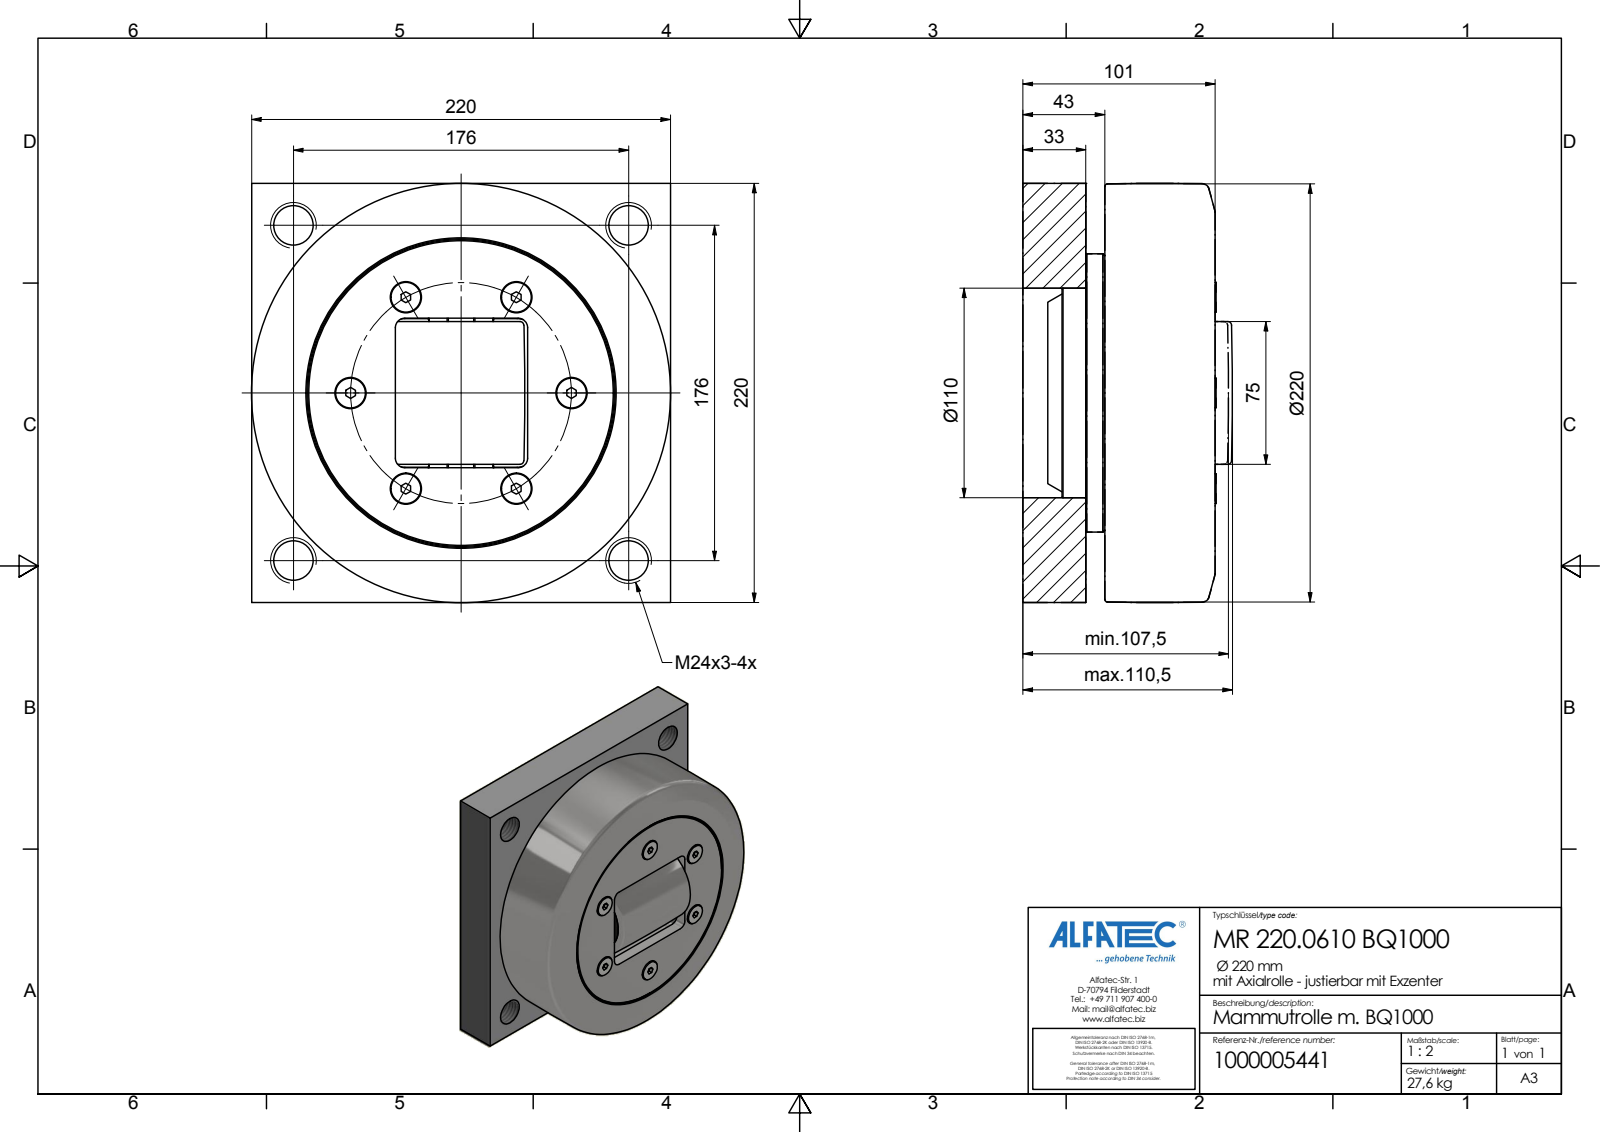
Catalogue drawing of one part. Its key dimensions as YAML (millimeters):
part_name: "MR 220.0610 BQ1000_Kontur"
step_written_by: "Autodesk Inventor 2020 (AUTOMOTIVE_DESIGN)"
units: millimeters
bodies: {solids: 1, faces: 302, planar: 130, cylindrical: 93, other: 79}
overall_size: [220, 220, 110.06]
volume: 3170000
surface_area: 366567
round_holes:
  - {diameter: 8.5, count: 6}
  - {diameter: 20.75, count: 4}
  - {diameter: 2.5, count: 1}
  - {diameter: 4.92, count: 1}
  - {diameter: 15, count: 1}
  - {diameter: 110, count: 1}
  - {diameter: 162, count: 1}
  - {diameter: 173.3, count: 1}
round_bosses_or_shafts:
  - {diameter: 15.6, count: 6}
  - {diameter: 8, count: 6}
  - {diameter: 161, count: 1}
  - {diameter: 148, count: 1}
  - {diameter: 146, count: 1}
  - {diameter: 130, count: 1}
  - {diameter: 3, count: 1}
partial_cylinders:
  - {radius: 0.5, count: 14}
  - {radius: 2, count: 4}
  - {radius: 3.25, count: 4}
  - {radius: 5, count: 4}
  - {radius: 10, count: 4}
  - {radius: 3.5, count: 1}
  - {radius: 18.25, count: 1}
face_to_face_distances: [33, 43, 10, 220, 67.7, 100.7, 57.7, 10.7, 47, 1.5]
hole_center_spacings: [58, 100.46, 70.05, 92.97, 122.95, 124.45, 150.29, 170.47]
